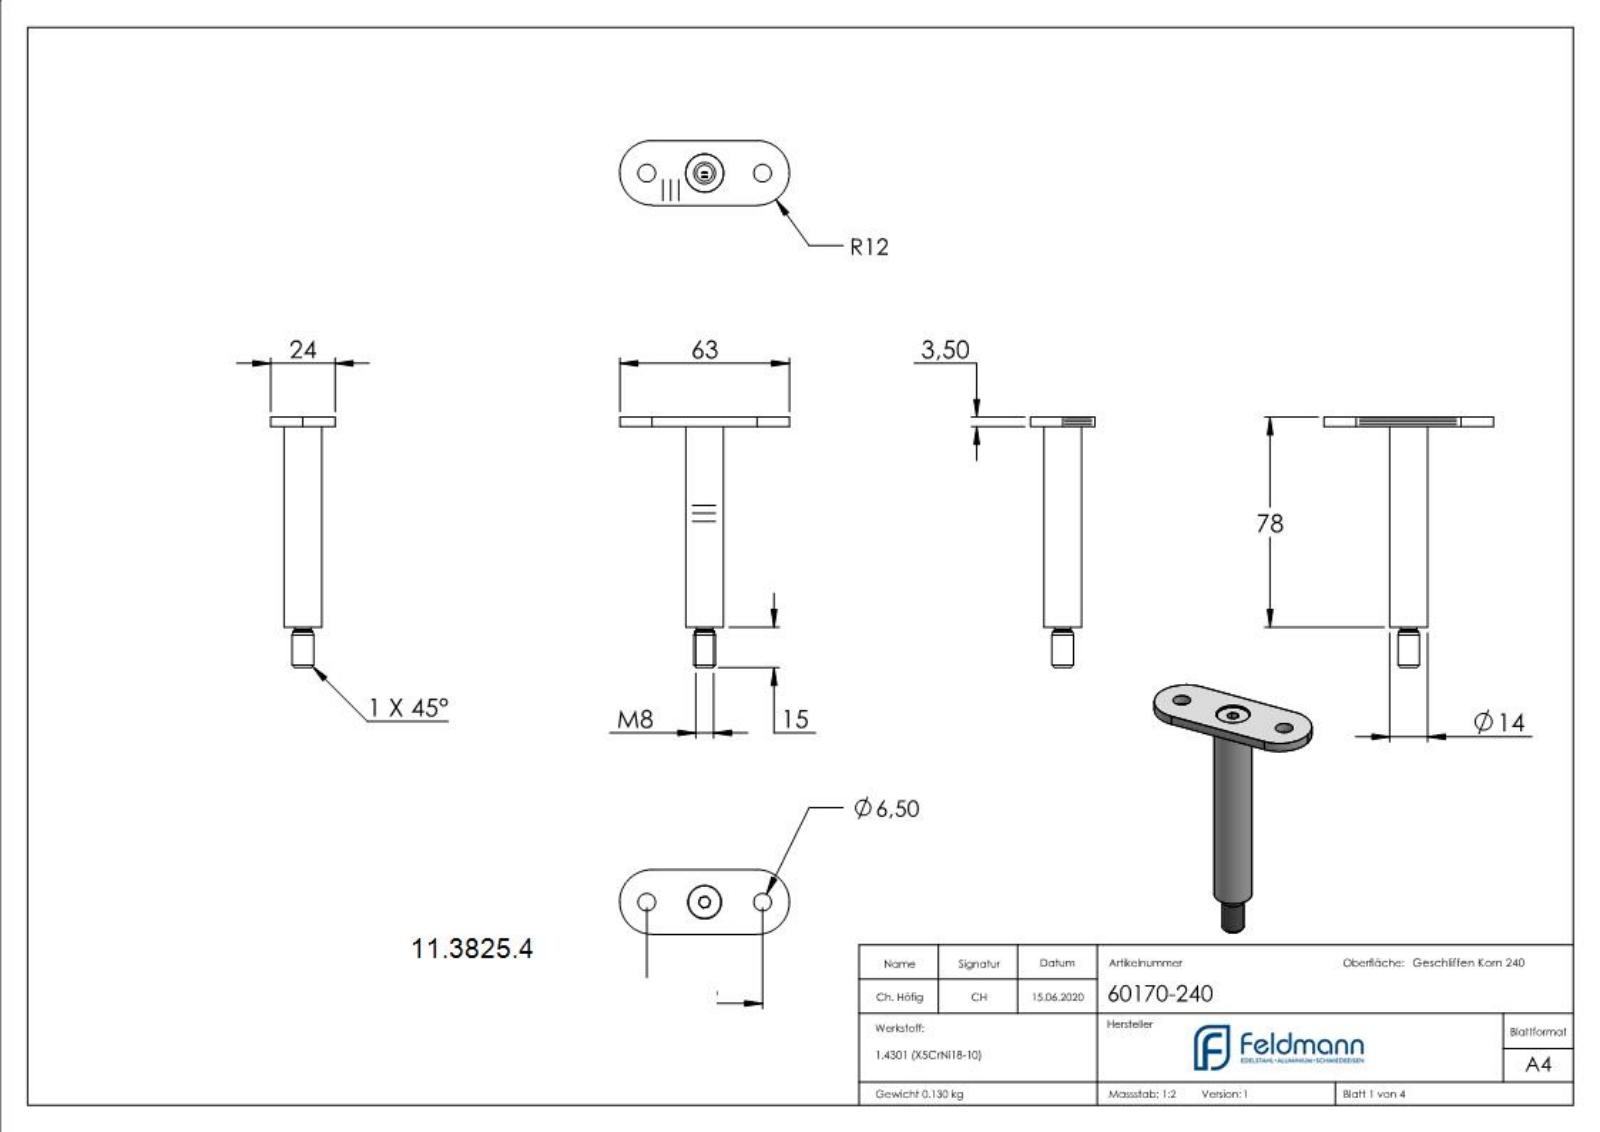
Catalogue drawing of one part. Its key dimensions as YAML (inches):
part_name: "60180-240_60180-240; DIN-7991_-_DIN7991 M6x16_DIN7991 M6x16; 50236-Konfig_50233-240; 60170-240"
step_written_by: "SolidWorks 2015 (CONFIG_CONTROL_DESIGN)"
units: inches
bodies: {solids: 3, faces: 280, planar: 138, cylindrical: 24, other: 118}
overall_size: [3.661, 2.48, 0.945]
volume: 1.007
surface_area: 12.63
round_holes:
  - {diameter: 0.256, count: 2}
  - {diameter: 0.197, count: 1}
  - {diameter: 0.492, count: 1}
  - {diameter: 0.559, count: 1}
round_bosses_or_shafts:
  - {diameter: 0.551, count: 1}
  - {diameter: 0.472, count: 1}
  - {diameter: 0.315, count: 1}
  - {diameter: 0.236, count: 1}
partial_cylinders:
  - {radius: 0.472, count: 2}
face_to_face_distances: [0.138, 0.118, 0.02, 0.945, 0.028, 0.11, 0.091, 3.524, 3.543, 3.634]
hole_center_spacings: [0.846, 1.693]
